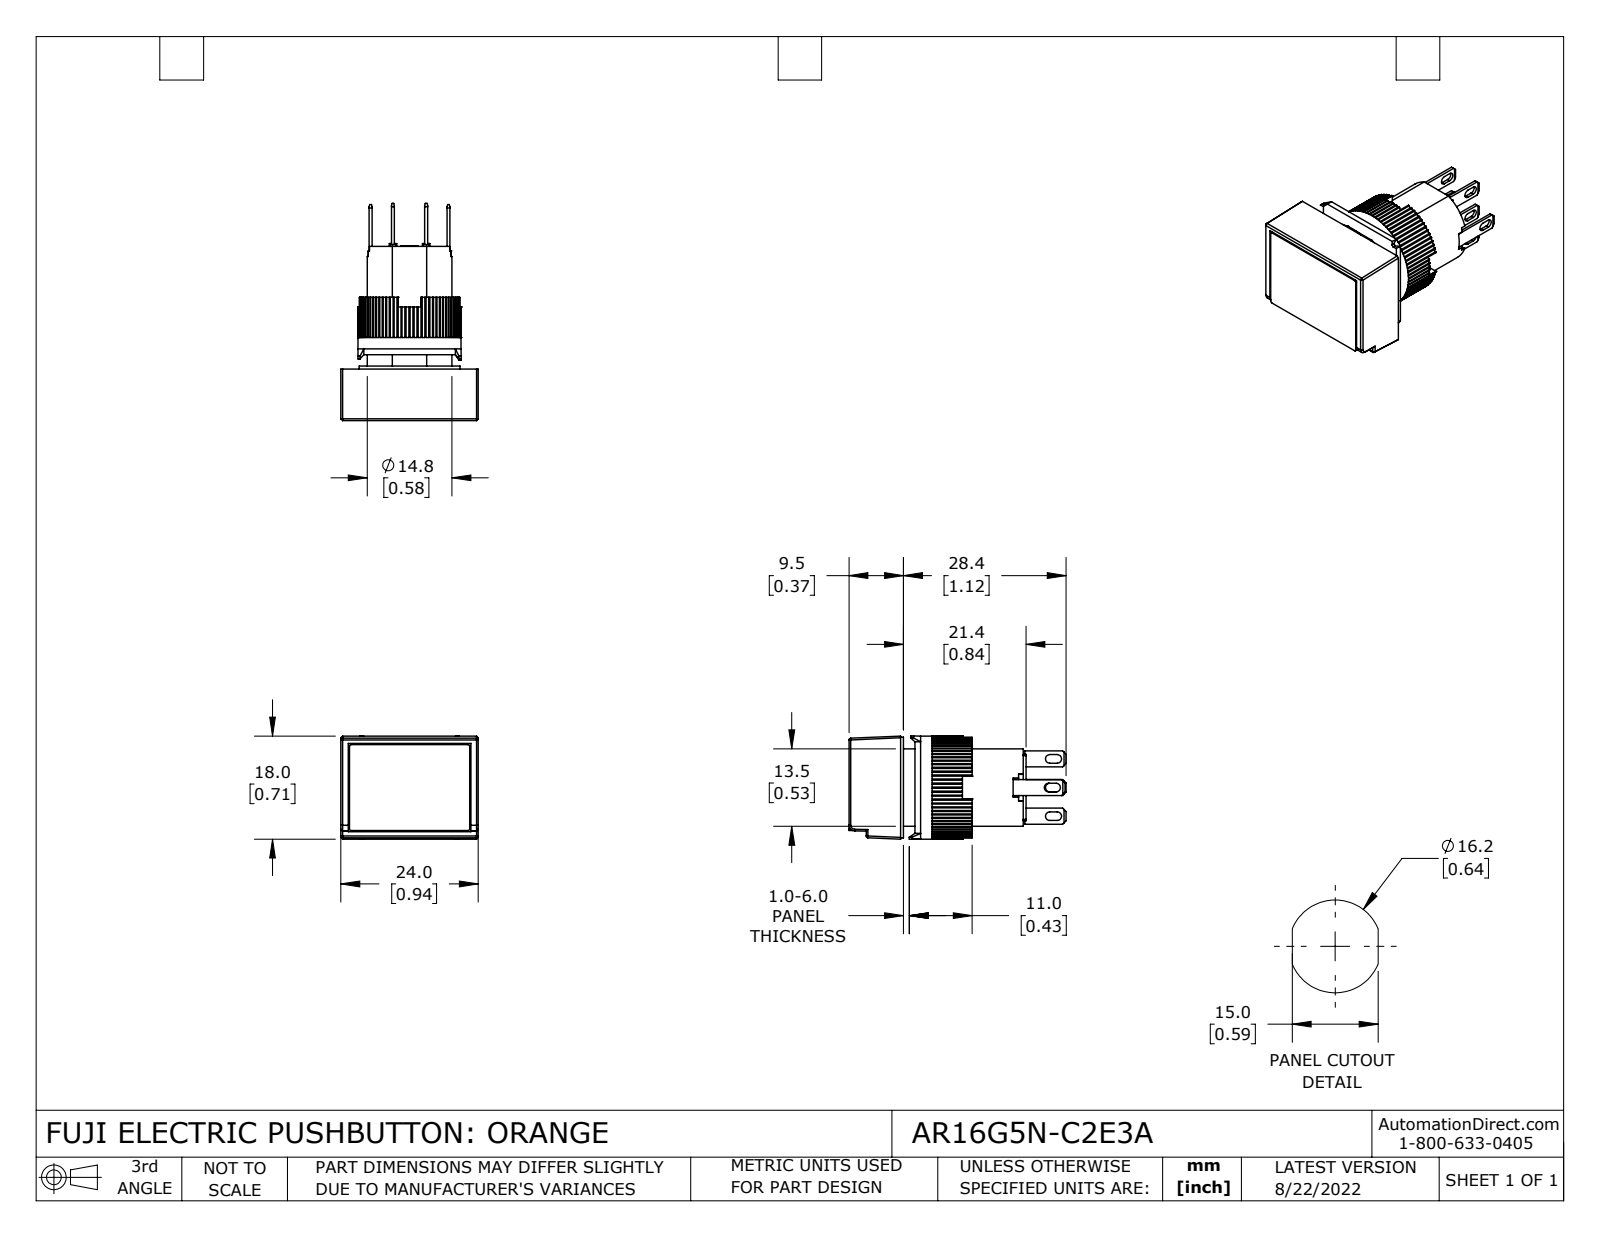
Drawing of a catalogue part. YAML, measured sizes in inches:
part_name: "AR16G5N-C2E3A"
step_written_by: "SolidWorks 2021 (CONFIG_CONTROL_DESIGN)"
units: inches
bodies: {solids: 14, faces: 841, planar: 654, cylindrical: 181, other: 6}
overall_size: [1.492, 0.945, 0.709]
volume: 0.448
surface_area: 9.503
round_holes:
  - {diameter: 0.543, count: 1}
  - {diameter: 0.583, count: 1}
round_bosses_or_shafts:
  - {diameter: 0.709, count: 1}
  - {diameter: 0.693, count: 1}
partial_cylinders:
  - {radius: 0.01, count: 80}
  - {radius: 0.008, count: 12}
  - {radius: 0.03, count: 8}
  - {radius: 0.012, count: 6}
  - {radius: 0.039, count: 1}
face_to_face_distances: [0.213, 0.354, 0.142, 0.35, 0.492, 0.138, 0.02, 0.843, 0.059, 0.453]
